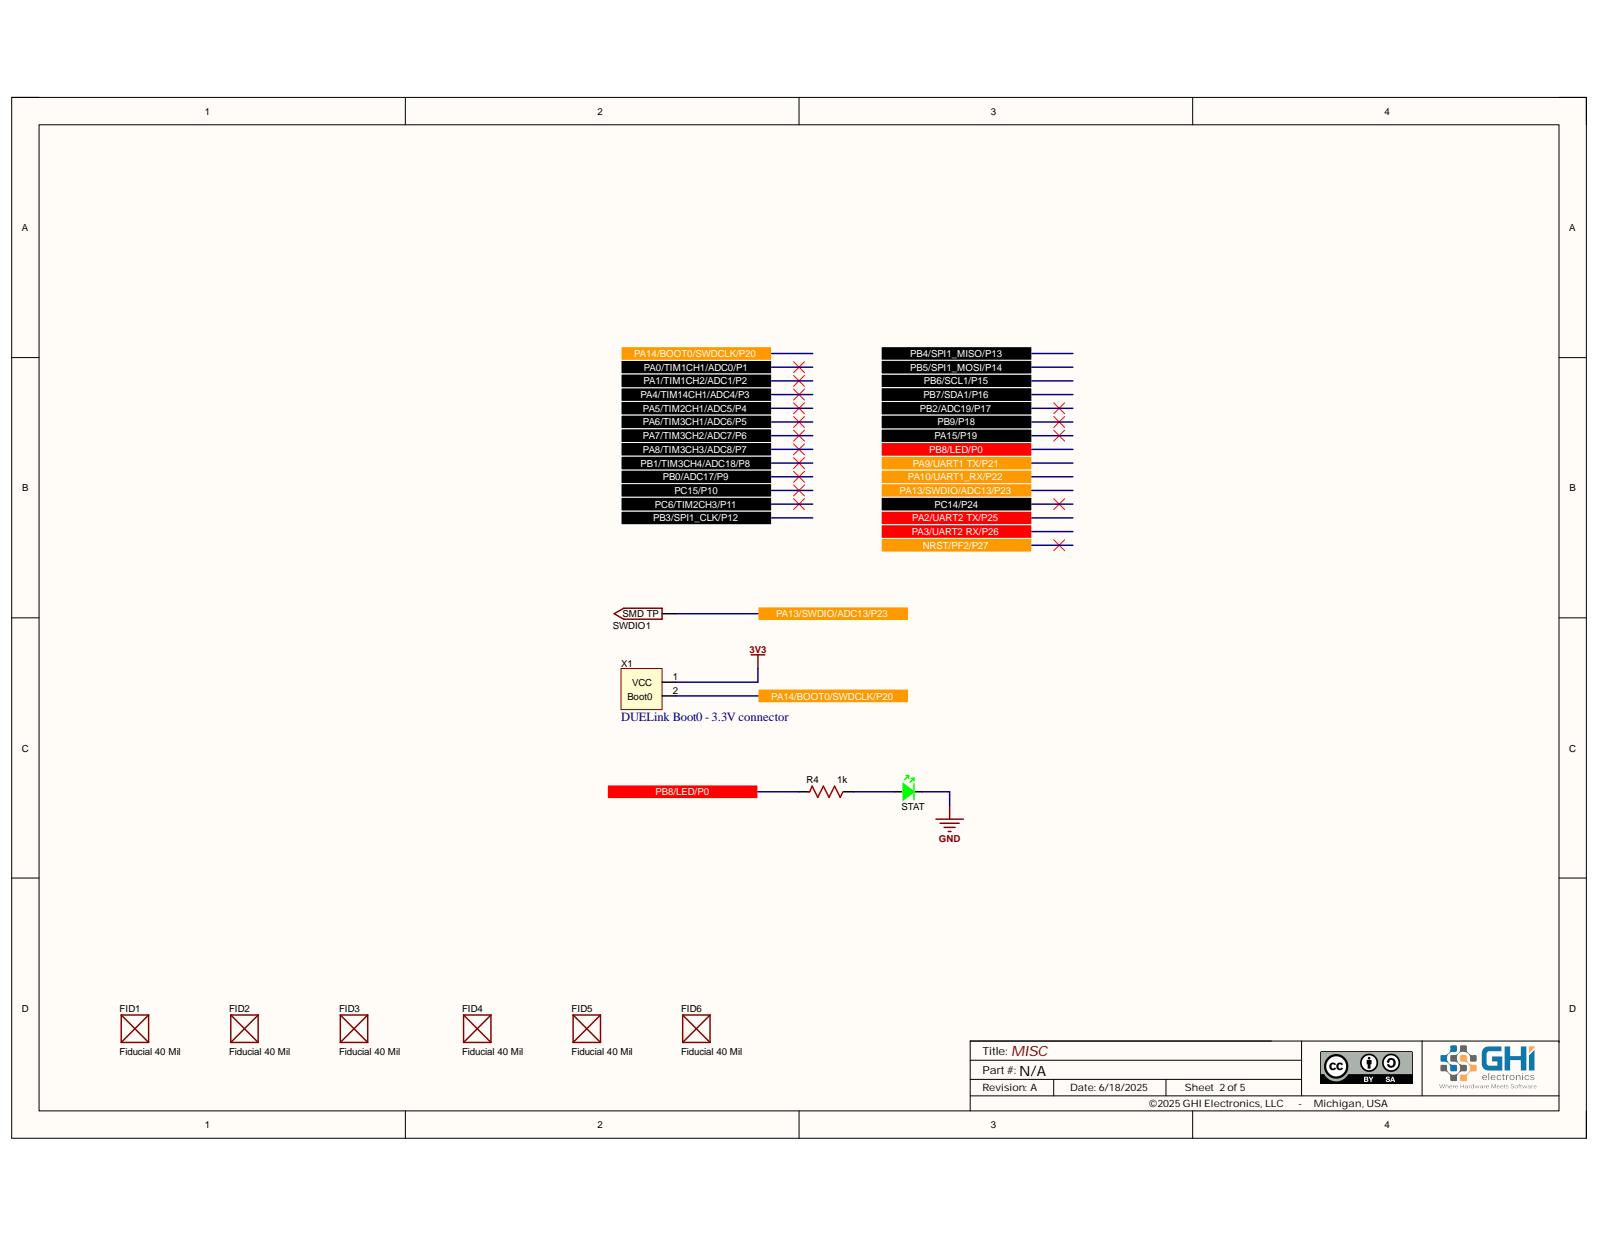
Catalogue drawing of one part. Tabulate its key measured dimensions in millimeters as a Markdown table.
| quantity | value |
| --- | --- |
| part name | PCB; Board; J11; Conn_Harwin_M20-9990846_eec (+7 more) |
| STEP written by | Open CASCADE 7.5 (AUTOMOTIVE_DESIGN) |
| units | millimeters |
| bodies | 127 solids, 2570 faces (1720 planar, 583 cylindrical, 267 other) |
| overall size | 47 × 30.63 × 20.24 |
| volume | 2 167 mm³ |
| surface area | 6 602 mm² |
| round holes (diameter × count) | 1.02 × 16, 3 × 4, 1.02 × 2, 3.6 × 1, 4 × 1 |
| round bosses / shafts (diameter × count) | 1 × 5, 6 × 1 |
| partial cylindrical surfaces (radius × count) | 0.12 × 35, 0.15 × 14, 3.5 × 4, 0.17 × 2, 0.18 × 2, 0.18 × 2, 0.5 × 2 |
| main face-to-face distances | 11.69, 11.49, 9.89, 10.09, 1.6, 5, 6.6, 16.69, 16.49, 0.5 |
| hole center spacings | 2.54, 5.08, 7.62, 10.16, 2.53, 2.55, 5.07, 5.09 |
